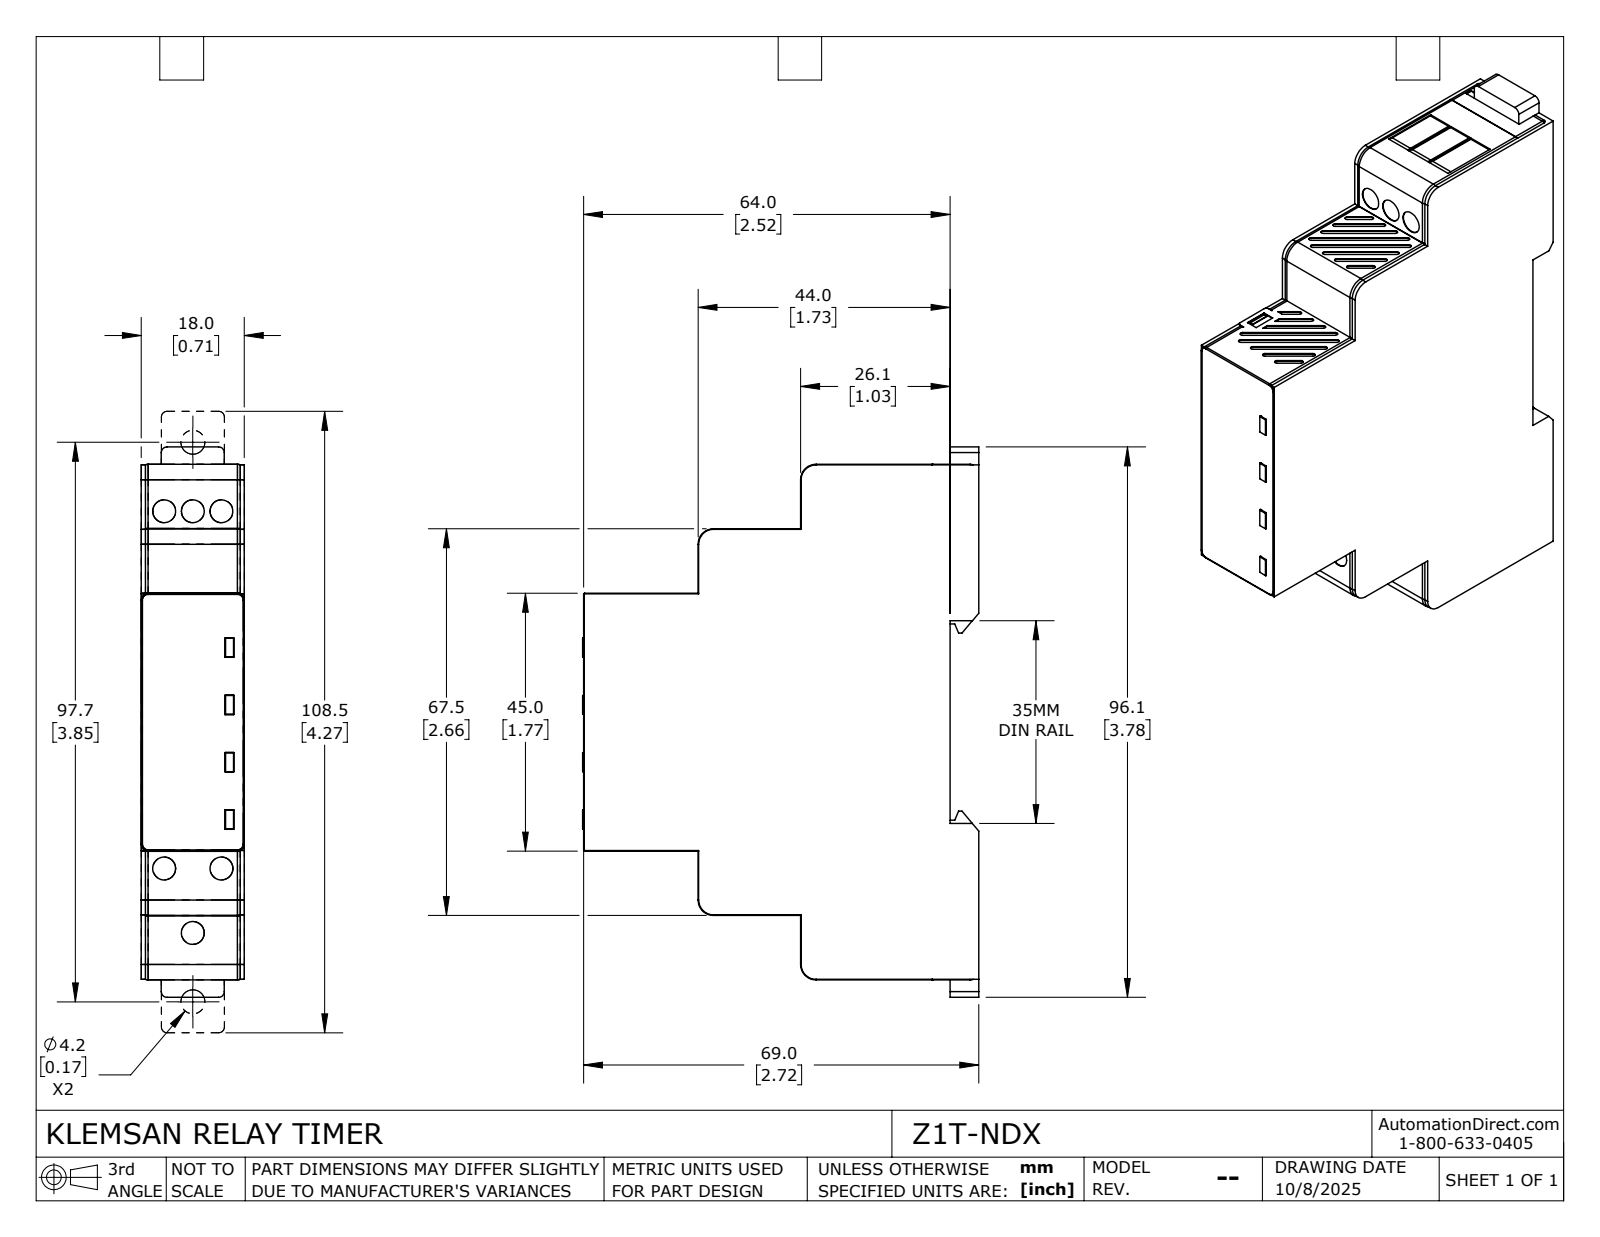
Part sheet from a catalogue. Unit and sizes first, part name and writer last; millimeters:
Units: millimetres
Overall size (bounding box): 96.07 × 69.15 × 18
Round holes (diameter × count): ⌀4.2 ×2, ⌀4 ×1
Partial cylindrical surfaces — rounded edges, fillets, slot ends (radius × count): R1.2 ×16, R0.2 ×4, R1 ×4, R2.6 ×4, R2.7 ×4, R0.5 ×2, R1.5 ×2
Main face-to-face distances: 18, 3.5, 14.5, 11.25, 64, 5, 69, 22.5, 67.4, 67.5
Hole centre spacings: 5.83, 79.43, 85.26
Volume: 83 847 mm³ · Surface area: 17 884 mm²
Bodies: 3 solids, 440 faces (280 planar, 60 cylindrical, 100 other)
Part name (STEP PRODUCT): Z1T-NDX
STEP written by: SolidWorks 2024 (CONFIG_CONTROL_DESIGN)
